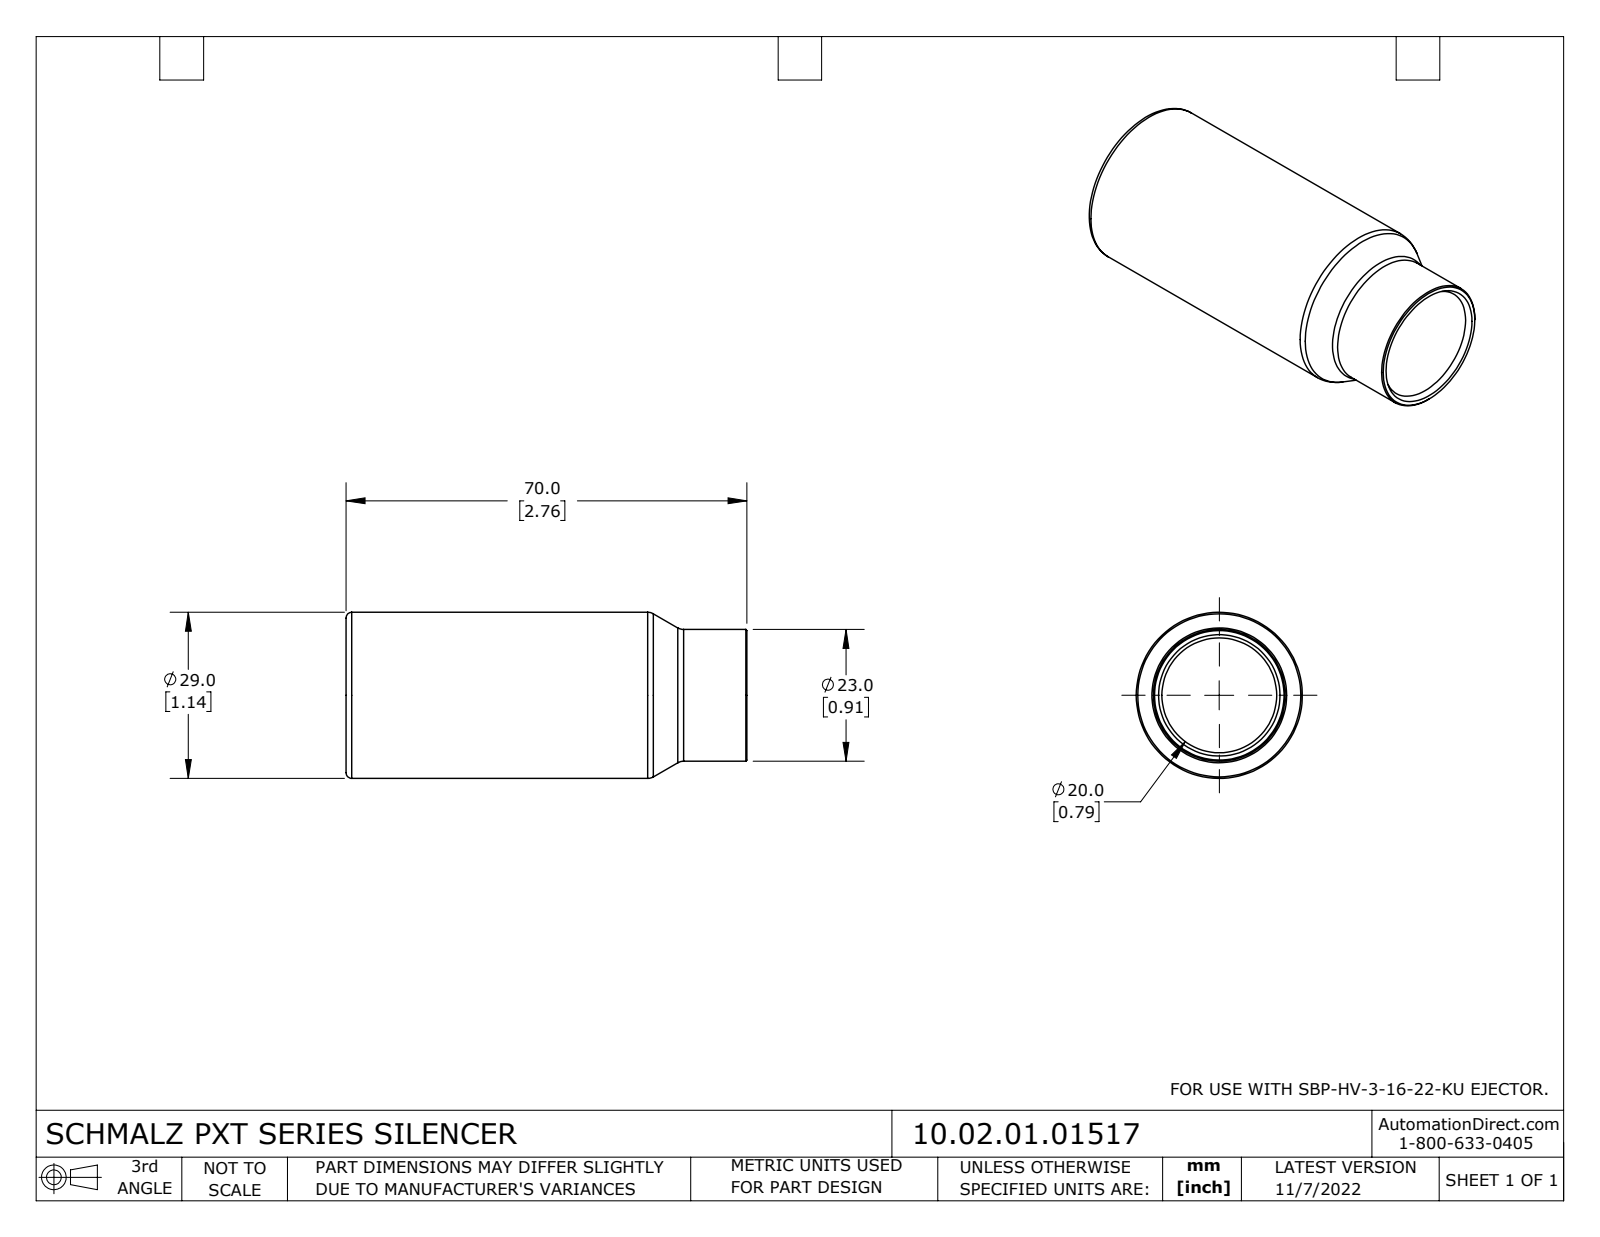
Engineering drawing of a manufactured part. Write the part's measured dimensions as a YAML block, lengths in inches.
part_name: "10.02.01.01517"
step_written_by: "SolidWorks 2021 (CONFIG_CONTROL_DESIGN)"
units: inches
bodies: {solids: 1, faces: 27, planar: 5, cylindrical: 8, other: 14}
overall_size: [2.756, 1.142, 1.142]
volume: 2.563
surface_area: 12.17
round_holes:
  - {diameter: 0.63, count: 1}
round_bosses_or_shafts:
  - {diameter: 1.142, count: 1}
  - {diameter: 0.906, count: 1}
  - {diameter: 0.835, count: 1}
face_to_face_distances: [2.717, 0.039, 2.677, 0.591, 2.087, 2.126, 0.63, 2.756]
